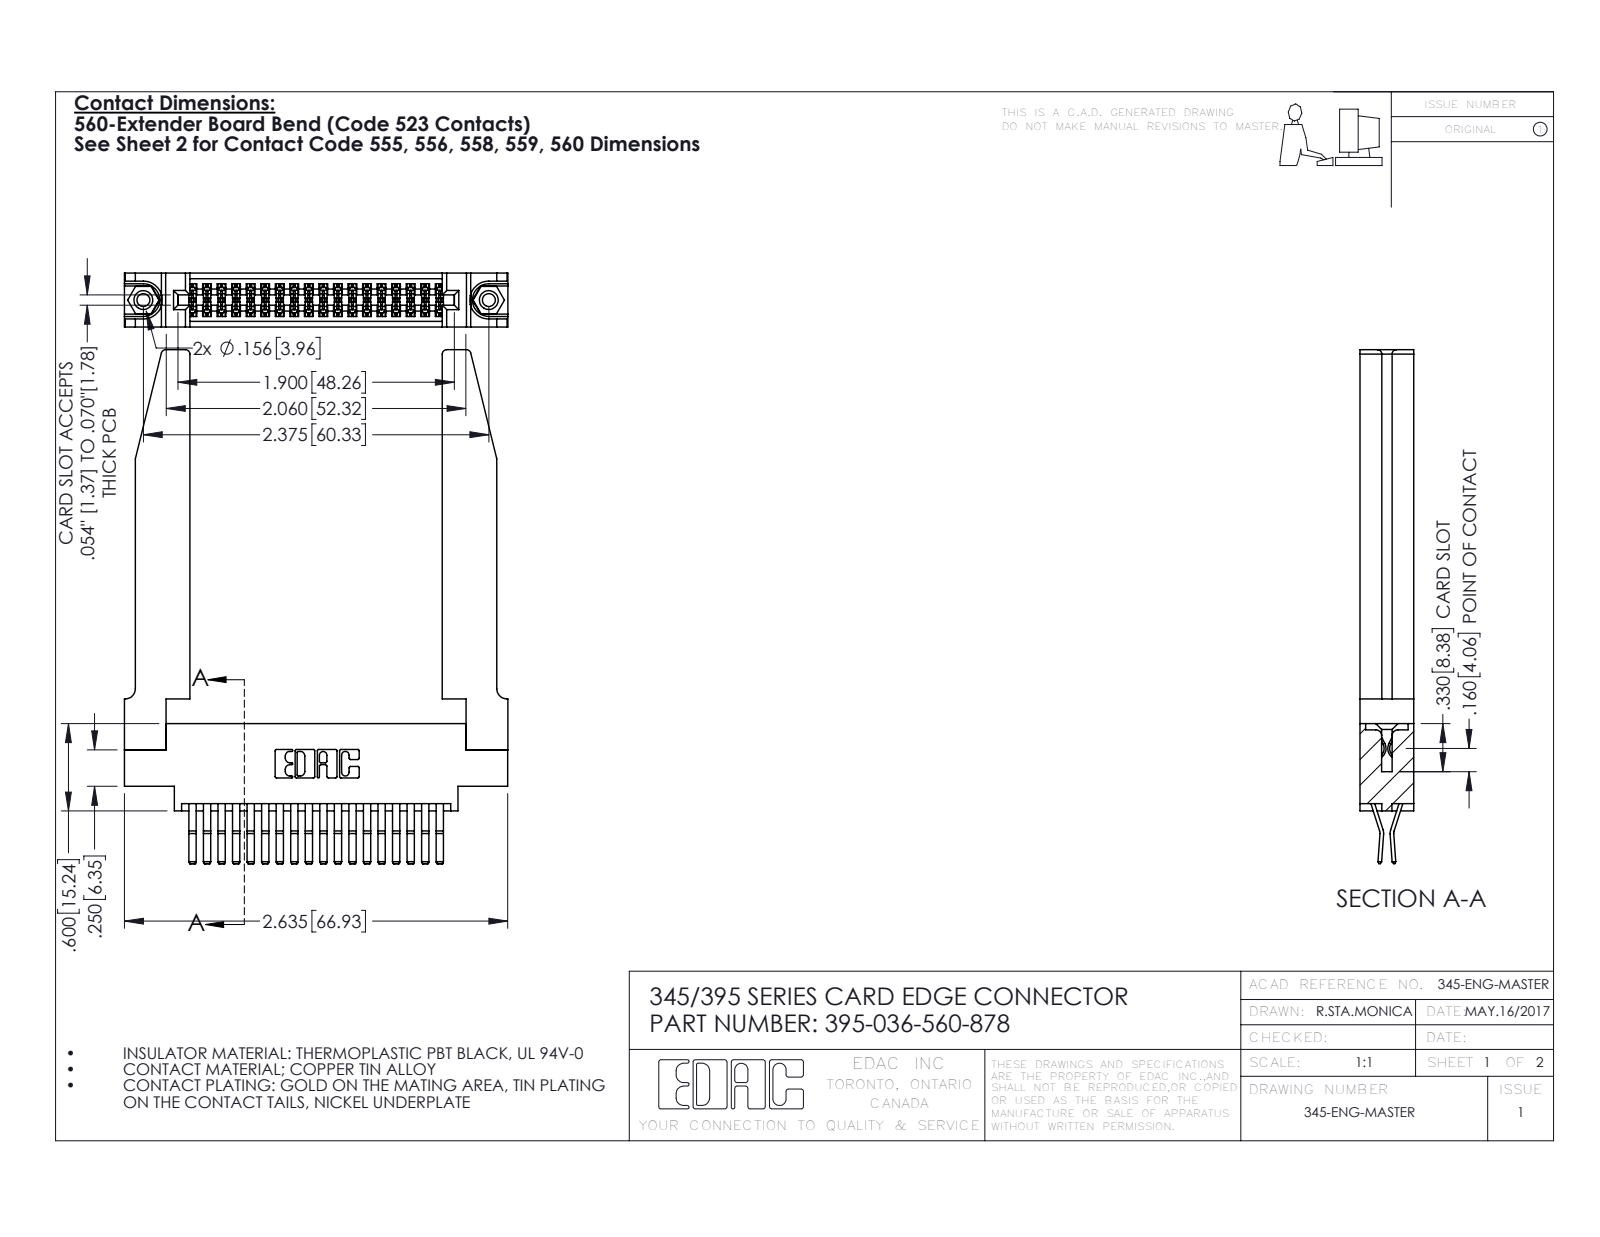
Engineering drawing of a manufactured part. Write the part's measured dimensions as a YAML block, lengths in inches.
part_name: "345-220-078_345-220-078; 345-292-001_560 Tail; 395-036-560-878; 345 Part_0.170 Offset - 0.156 Dia-TH (+1 more)"
step_written_by: "SolidWorks 2016 (CONFIG_CONTROL_DESIGN)"
units: inches
bodies: {solids: 41, faces: 2236, planar: 1414, cylindrical: 770, other: 52}
overall_size: [3.532, 2.636, 0.37]
volume: 0.865
surface_area: 25.71
round_holes:
  - {diameter: 0.089, count: 2}
  - {diameter: 0.125, count: 2}
  - {diameter: 0.156, count: 2}
  - {diameter: 0.064, count: 1}
round_bosses_or_shafts:
  - {diameter: 0.155, count: 2}
partial_cylinders:
  - {radius: 0.006, count: 54}
  - {radius: 0.01, count: 22}
  - {radius: 0.03, count: 8}
  - {radius: 0.007, count: 6}
  - {radius: 0.031, count: 6}
  - {radius: 0.026, count: 3}
  - {radius: 0.01, count: 2}
  - {radius: 0.014, count: 2}
face_to_face_distances: [0.37, 0.072, 0.298, 0.025, 0.15, 0.148, 0.098, 0.272, 0.2, 0.225]
hole_center_spacings: [0.27, 2.141, 2.375]
